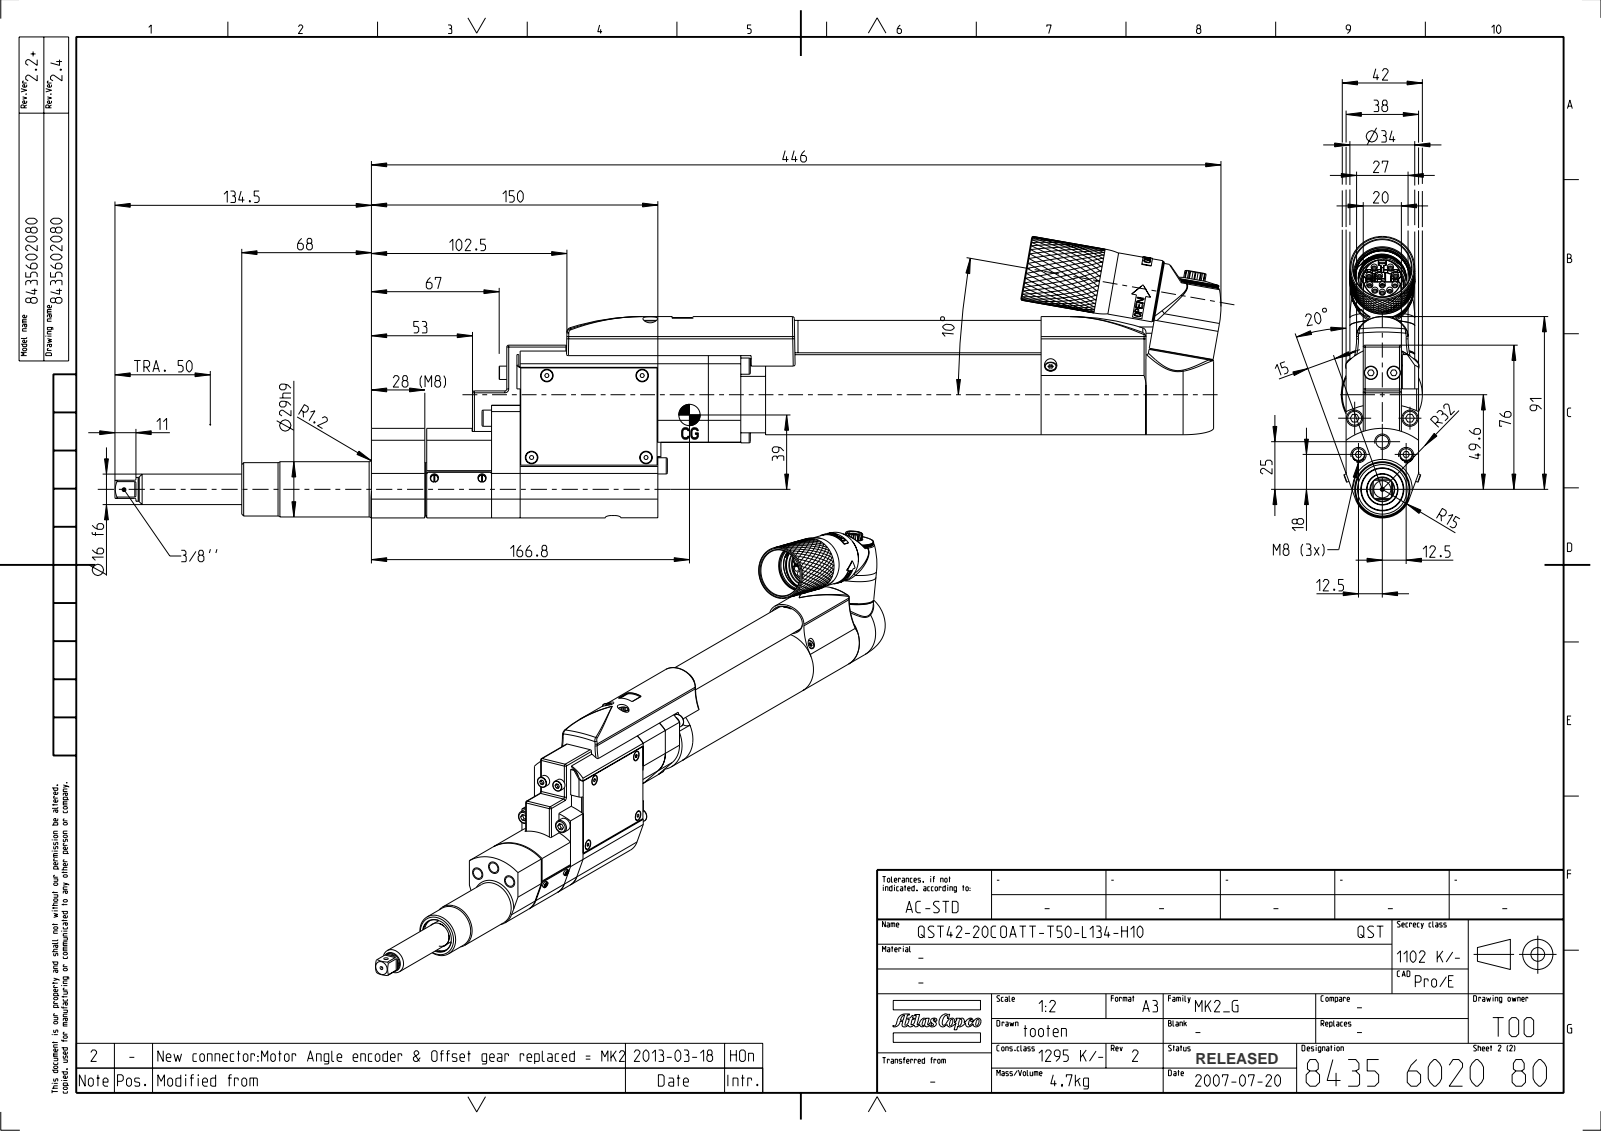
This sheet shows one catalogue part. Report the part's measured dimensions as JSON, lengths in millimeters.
{"part_name": "4230260102; 4230260112_ASM; 4230262500; 0219110017 (+8 more)", "step_written_by": "PRO/ENGINEER BY PARAMETRIC TECHNOLOGY CORPORATION, 2012420 (CONFIG_CONTROL_DESIGN)", "units": "millimeters", "bodies": {"solids": 46, "faces": 4977, "planar": 1946, "cylindrical": 1427, "other": 1604}, "overall_size": [580.01, 147.69, 42], "volume_mm3": 525899, "surface_area_mm2": 299172, "round_holes": [[2.64, 11], [3.27, 11], [3.6, 11], [3, 8], [3.24, 8], [3.3, 7], [4.5, 7], [3.5, 5], [3.92, 5], [5.3, 5], [5.5, 5], [1.92, 4]], "round_bosses_or_shafts": [[3, 9], [5, 8], [8.5, 7], [4, 7], [6, 5], [34, 4], [7, 4], [4.2, 4]], "partial_cylinders_radius": [[1, 97], [0.1, 53], [2, 19], [0.29, 12], [0.51, 12], [0.2, 8], [0.5, 7], [0.6, 5]], "face_to_face_distances": [1, 37, 38, 9, 28, 29, 25, 19, 0.5, 72.2], "hole_center_spacings": [25, 7.16, 7.42, 15.92, 7.35, 19.03, 40.04, 15]}
